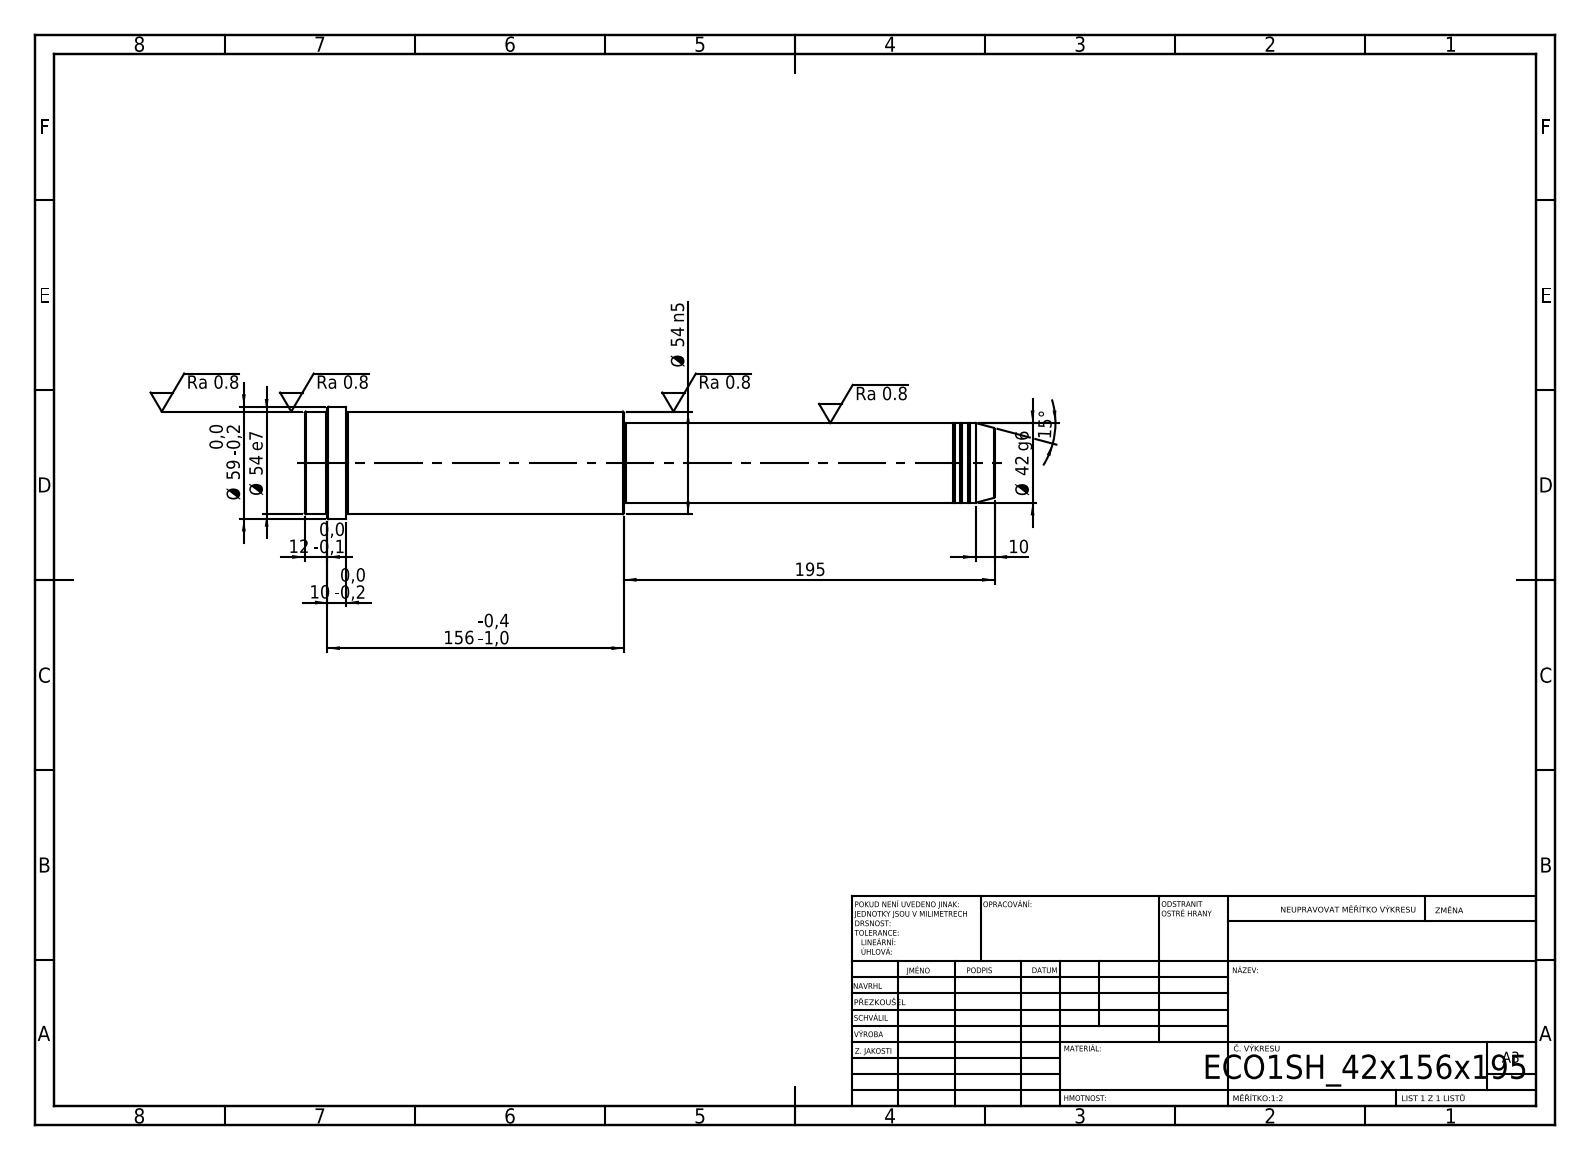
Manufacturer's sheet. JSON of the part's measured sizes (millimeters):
{"step_written_by": "SolidWorks 2019 (CONFIG_CONTROL_DESIGN)", "units": "millimeters", "bodies": {"solids": 1, "faces": 52, "planar": 6, "cylindrical": 16, "other": 30}, "overall_size": [363, 59, 59], "volume_mm3": 657244, "surface_area_mm2": 59847, "round_bosses_or_shafts": [[59, 1], [54, 1], [42, 1], [41, 1]], "face_to_face_distances": [363, 195, 168, 341, 146, 22, 351, 156, 10, 12]}
